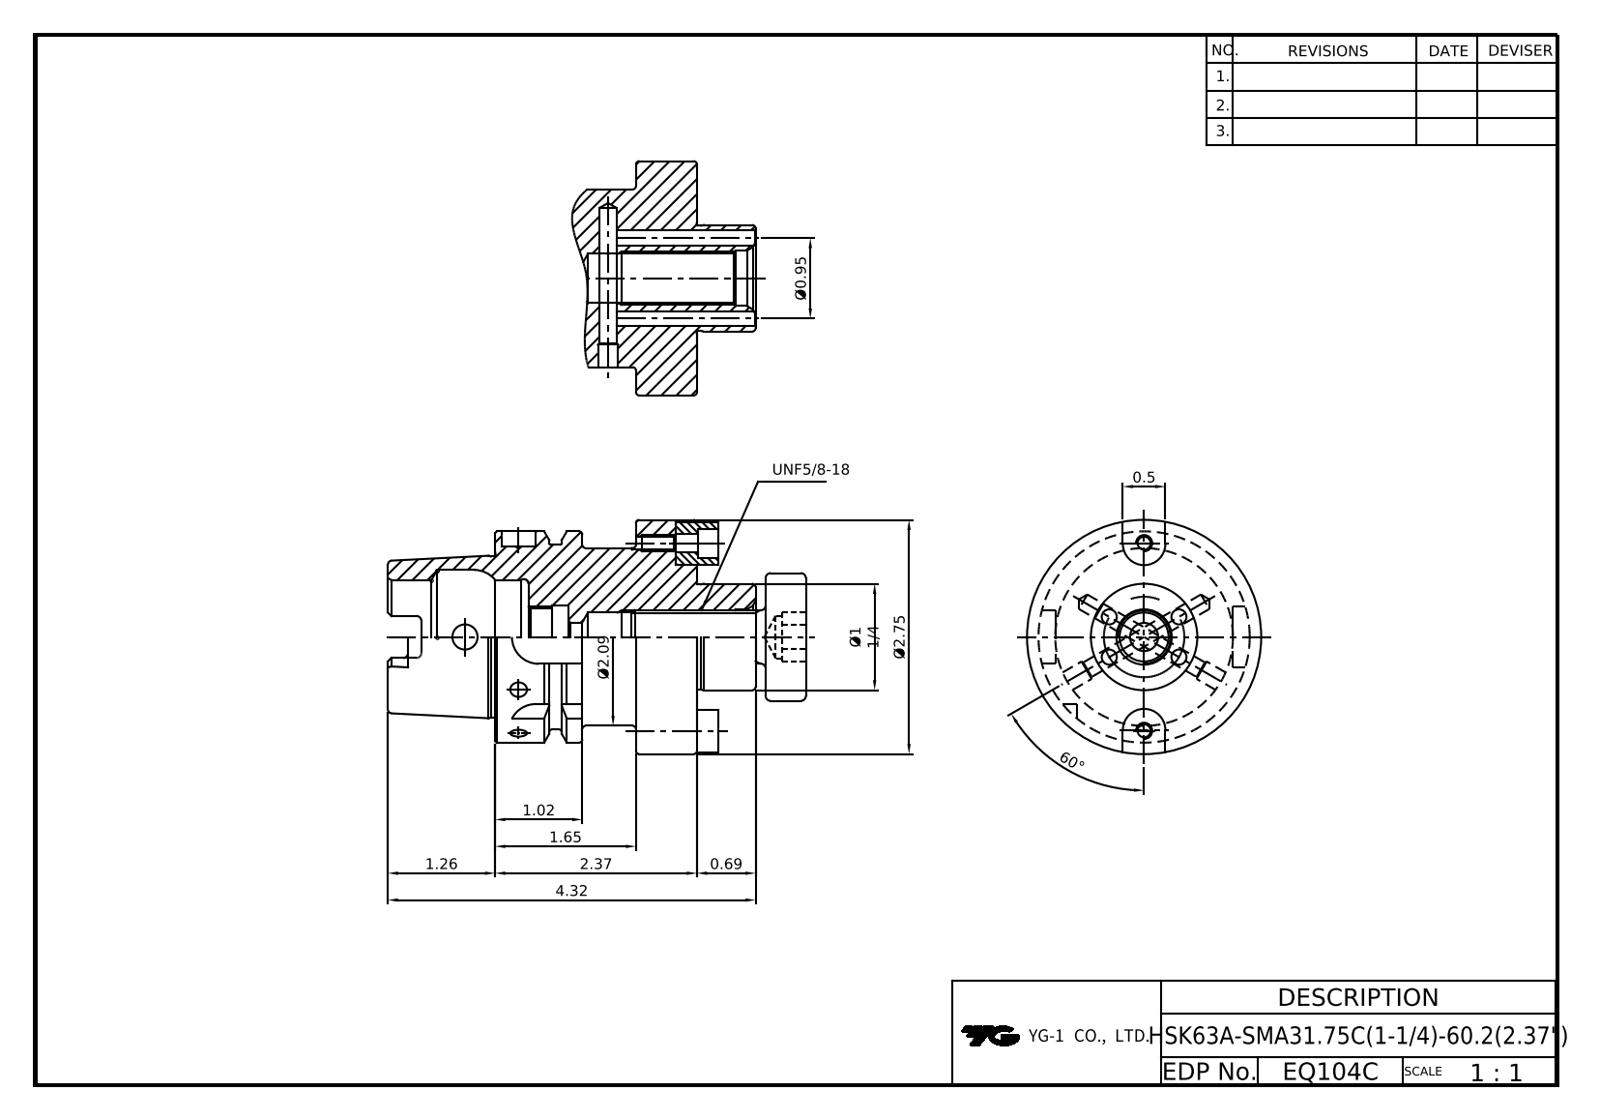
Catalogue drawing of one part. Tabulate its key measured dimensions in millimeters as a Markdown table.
| quantity | value |
| --- | --- |
| part name | LO-HSK63A-SMA31.75C-60.2; COLLAR BOLT-UNF5_8-18x40L; DRIVE KEY-12.7x12.7x12.7; HEX'' WRENCH BOLT-UNC#10-24x1_2L |
| STEP written by | Autodesk Inventor 2025 (AUTOMOTIVE_DESIGN) |
| units | millimeters |
| bodies | 6 solids, 220 faces (95 planar, 56 cylindrical, 69 other) |
| overall size | 126.7 × 69.9 × 69.9 |
| volume | 210 400 mm³ |
| surface area | 47 970 mm² |
| round holes (diameter × count) | 4.5 × 4, 3.7 × 2, 5.5 × 2, 8.7 × 2, 7.5 × 1, 8 × 1, 10 × 1, 12.7 × 1, 14.4 × 1, 16.5 × 1, 16.9 × 1, 19 × 1 |
| round bosses / shafts (diameter × count) | 7.9 × 2, 4.8 × 2, 69.9 × 1, 63 × 1, 55 × 1, 53 × 1, 48 × 1, 38.1 × 1 |
| partial cylindrical surfaces (radius × count) | 1.5 × 6, 2.9 × 4, 6.4 × 4, 8 × 4 |
| main face-to-face distances | 18.2, 42, 16, 12, 32, 60.2, 94.7, 52.7, 34.5, 72.7 |
| hole center spacings | 12, 24.3, 24.3, 35.5, 35.5, 20.8, 24, 28 |
